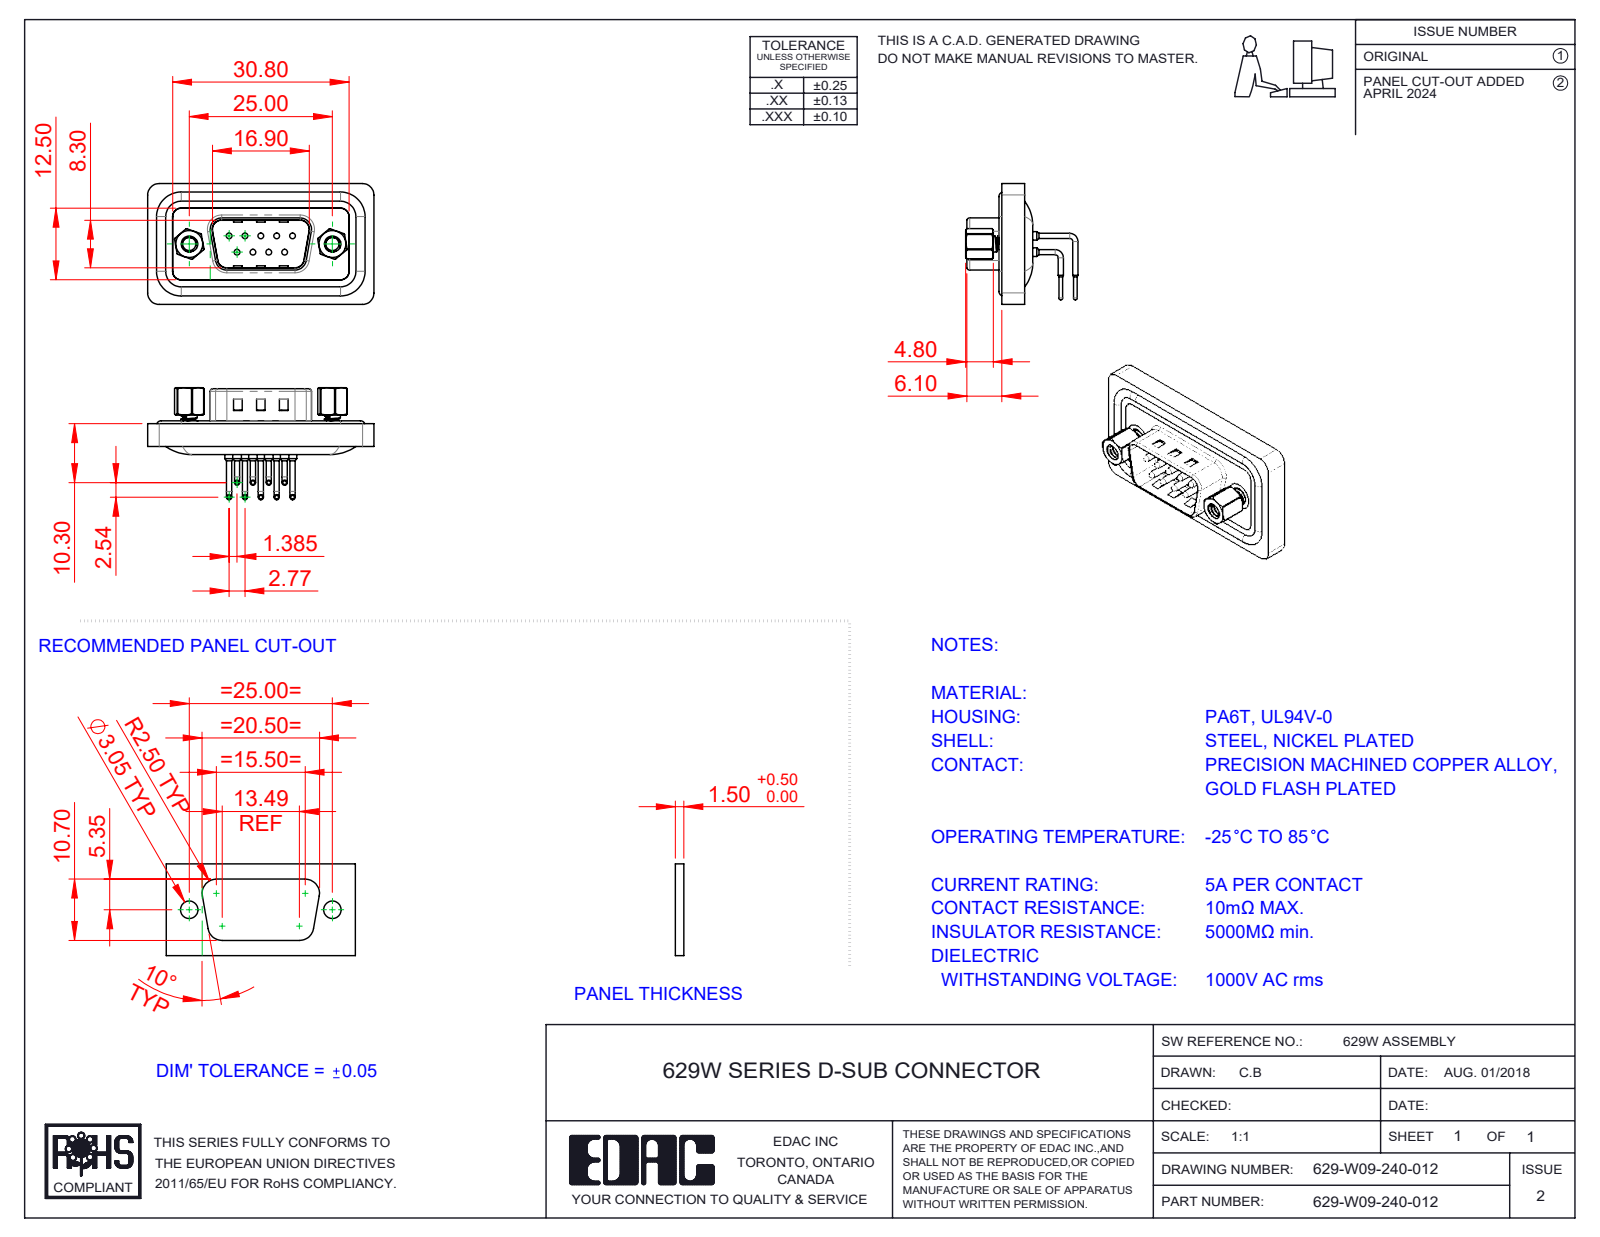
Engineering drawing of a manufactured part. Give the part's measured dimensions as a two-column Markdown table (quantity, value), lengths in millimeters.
| quantity | value |
| --- | --- |
| part name | 629W Contact Row 2; 629-W09-240-012; 629W Housing_09 Contacts; 629W Waterproof Housing_09 Contacts (+4 more) |
| STEP written by | SolidWorks 2016 (CONFIG_CONTROL_DESIGN) |
| units | millimeters |
| bodies | 17 solids, 1448 faces (717 planar, 546 cylindrical, 185 other) |
| overall size | 39.51 × 21.1 × 19.39 |
| volume | 4 014 mm³ |
| surface area | 6 674 mm² |
| round holes (diameter × count) | 1 × 9, 1.5 × 9, 1.7 × 9, 2 × 9, 2.26 × 2, 2.29 × 2, 4 × 2, 4.8 × 2, 5 × 2 |
| round bosses / shafts (diameter × count) | 0.9 × 18, 0.65 × 9, 1.6 × 4, 1.5 × 4, 4.9 × 2, 2.79 × 2, 5 × 1 |
| partial cylindrical surfaces (radius × count) | 1.5 × 14, 2 × 14, 1.01 × 9, 0.5 × 8, 2.7 × 6, 0.9 × 4, 1.6 × 4, 4.3 × 4 |
| main face-to-face distances | 0.4, 1.6, 1.1, 2.9, 2.5, 0.5, 4, 3.6, 4.3, 0.7 |
| hole center spacings | 3.16, 2.77, 5.54, 5.03, 5.04, 7.48, 7.49, 8.31 |
